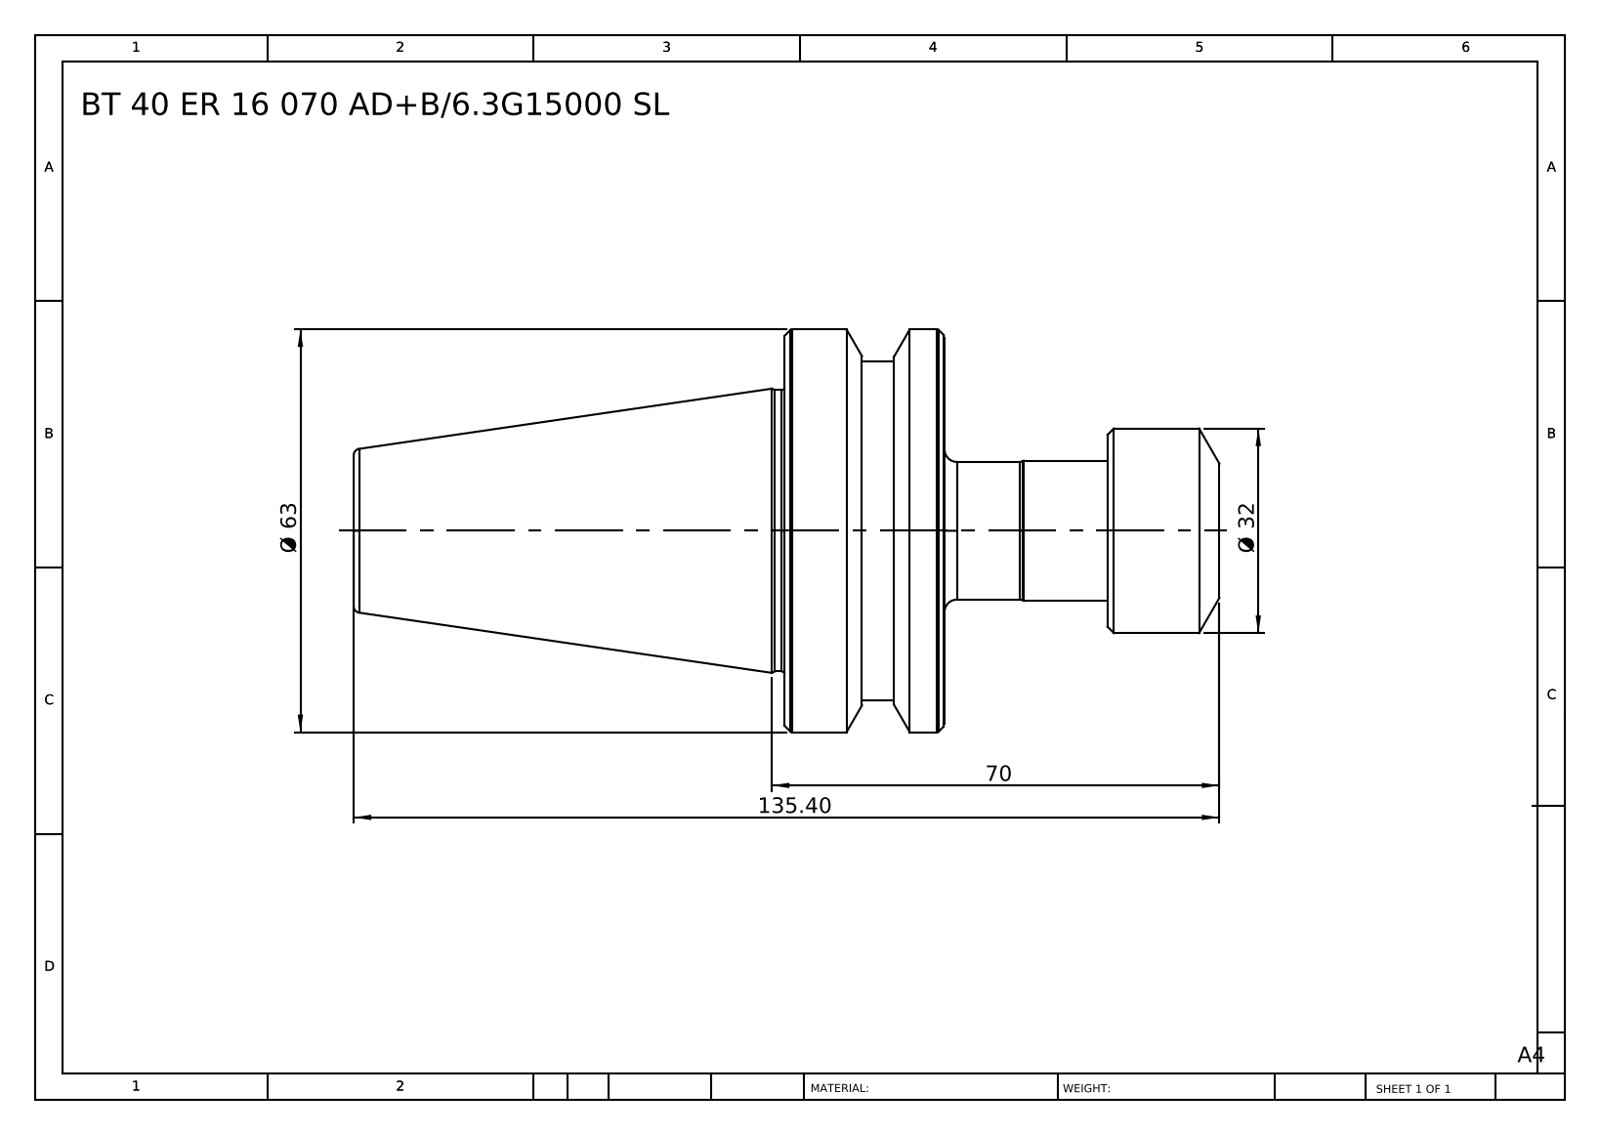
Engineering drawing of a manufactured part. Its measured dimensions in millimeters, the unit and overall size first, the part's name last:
Units: millimetres
Overall size (bounding box): 135.4 × 63 × 63
Round bosses / shafts (diameter × count): ⌀63 ×1, ⌀53 ×1, ⌀44 ×1, ⌀32 ×1, ⌀21.9 ×1, ⌀21.5 ×1
Main face-to-face distances: 25, 92.4, 67.4, 43, 68, 135.4, 17.5, 25.5, 50.5, 117.9
Volume: 161 158 mm³ · Surface area: 22 339 mm²
Bodies: 1 solid, 56 faces (7 planar, 14 cylindrical, 35 other)
Part name (STEP PRODUCT): BT40 ER 16 070 AD-6.3G15000 SL
STEP written by: SolidWorks 2014 (CONFIG_CONTROL_DESIGN)
